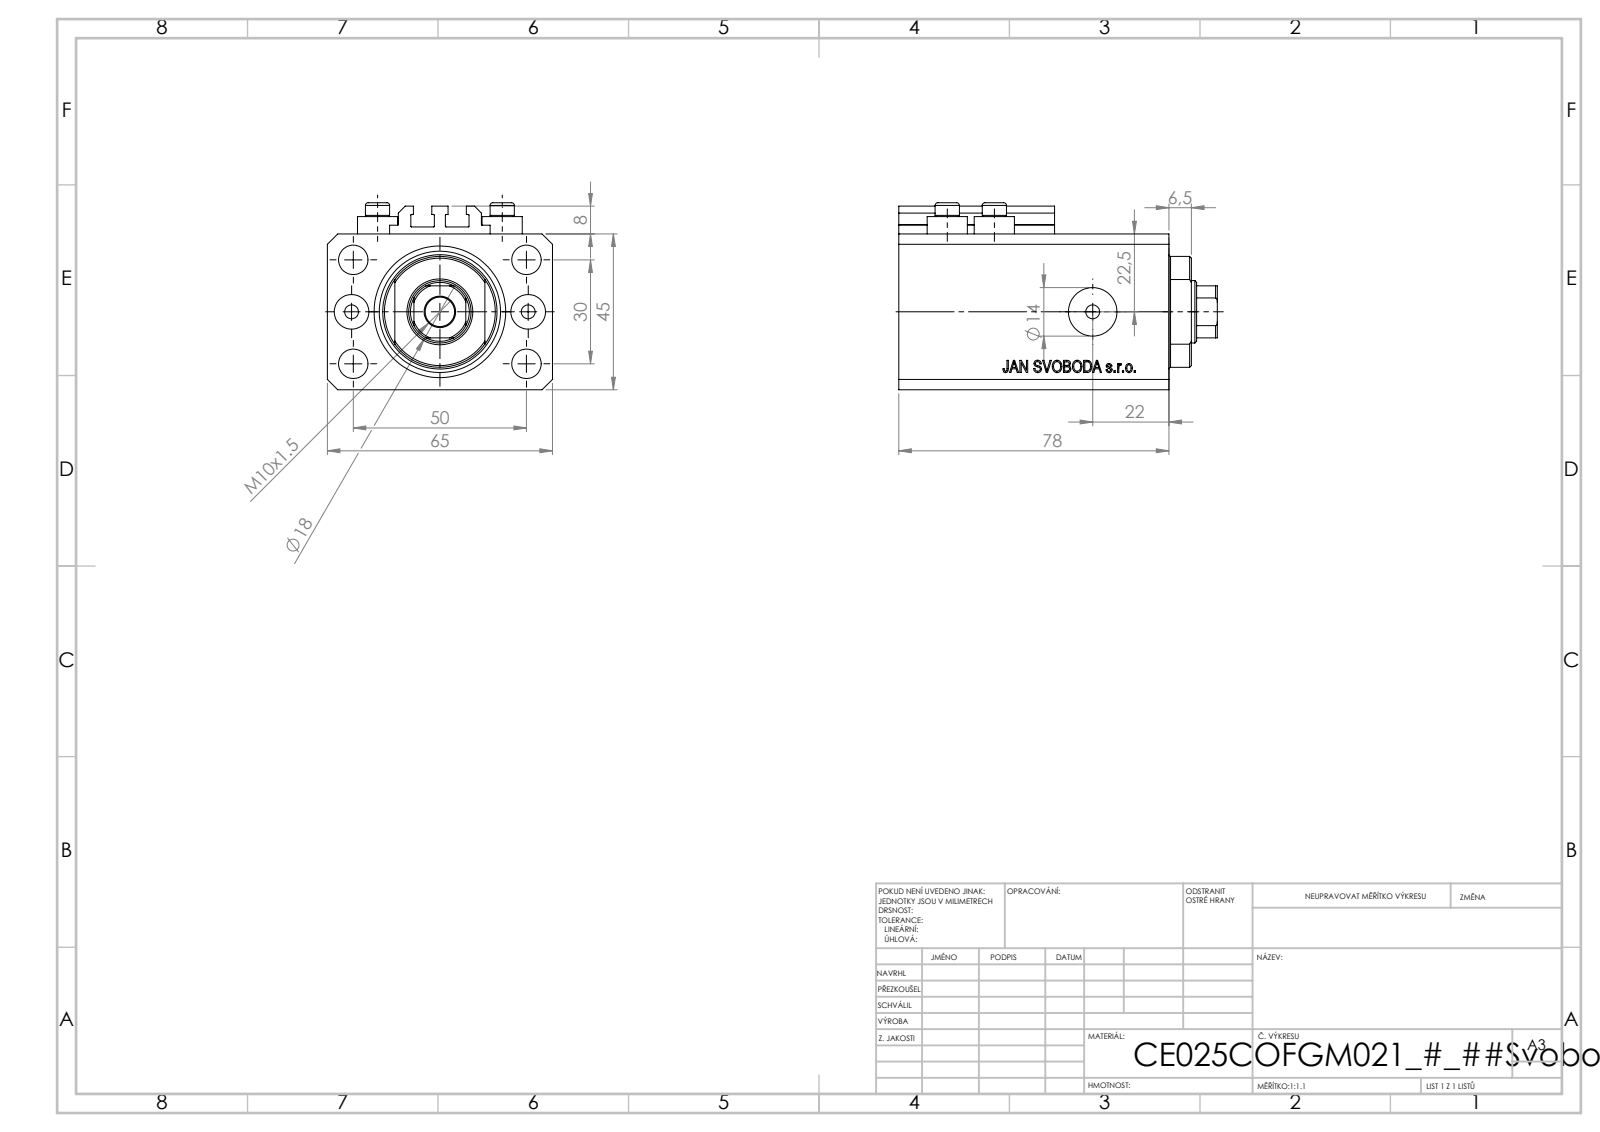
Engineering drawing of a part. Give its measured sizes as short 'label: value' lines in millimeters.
name: V250CE_C_VCP; V250CE_C_Body; V250CE_VC_C; ALLEN BOLT V250CE
written by: SolidWorks 2019 (CONFIG_CONTROL_DESIGN)
unit: mm
bodies: 8 solids, 1034 faces (504 planar, 86 cylindrical, 444 other)
size: 92 × 65 × 54
volume: 214 509 mm³; area: 57 821 mm²
holes: 8× ⌀4, 5× ⌀8.5, 2× ⌀10, 2× ⌀14, 1× ⌀18, 1× ⌀25, 1× ⌀38
bosses: 4× ⌀11.6, 4× ⌀7
rounds: 10× R0.2, 1× R8.5, 1× R16
face distances: 45, 65, 14, 64, 78, 6.9, 57.1, 71.1, 3, 47
hole spacings: 15.01, 29.15, 52.68, 13.6, 25.5, 30, 36, 38.48
